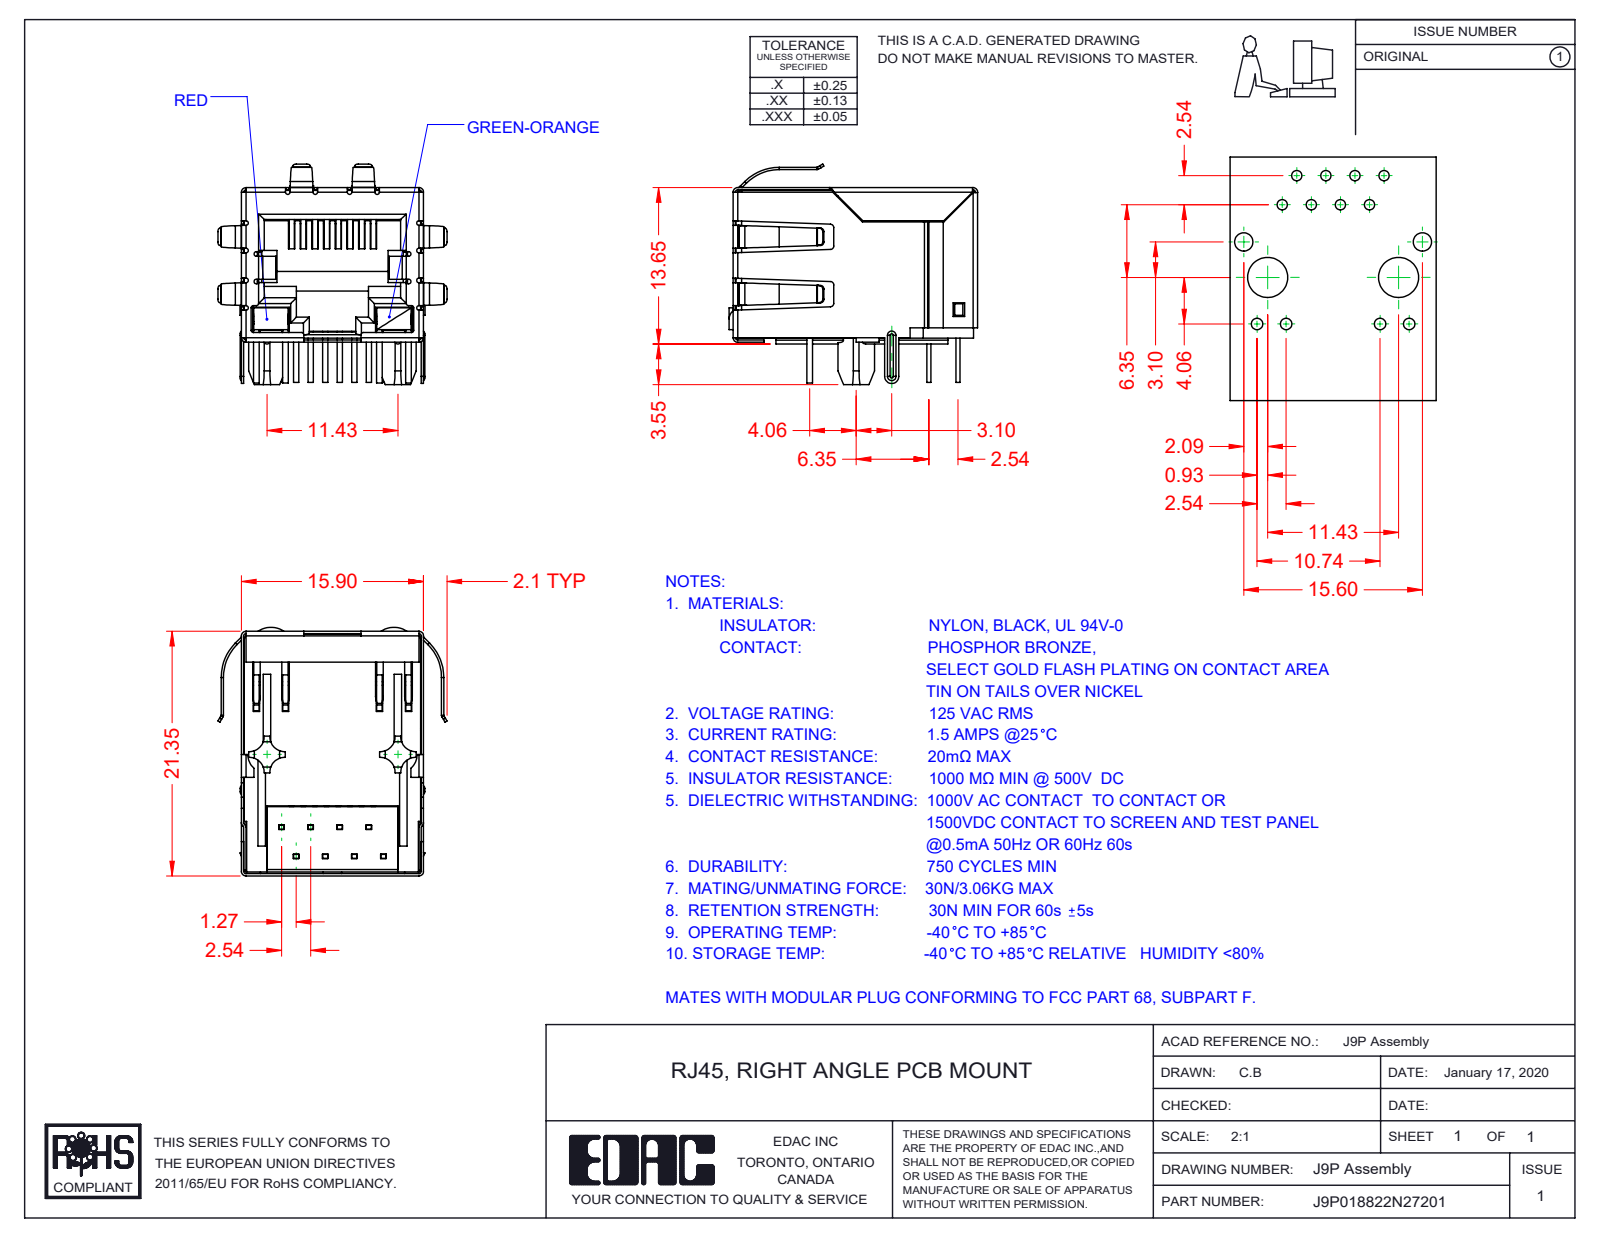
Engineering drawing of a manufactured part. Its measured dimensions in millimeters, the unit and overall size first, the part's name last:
Units: millimetres
Overall size (bounding box): 21.7 × 20 × 19.25
Partial cylindrical surfaces — rounded edges, fillets, slot ends (radius × count): R0.2 ×39, R0.5 ×22, R0.3 ×20, R0.4 ×16, R1.3 ×8, R0.23 ×5, R0.11 ×4, R0.31 ×4
Main face-to-face distances: 15.45, 15.7, 15.65, 0.35, 0.54, 15.5, 12.36, 0.6, 1.4, 0.59
Volume: 2 687 mm³ · Surface area: 7 515 mm²
Bodies: 13 solids, 1474 faces (1042 planar, 338 cylindrical, 94 other)
Part name (STEP PRODUCT): 9P-LED LED RH_7-Green-Orange; 9P-LED LED LH_2-Red; 9P-LED Assembly; 9P-LED Contacts (+4 more)
STEP written by: SolidWorks 2016 (CONFIG_CONTROL_DESIGN)
